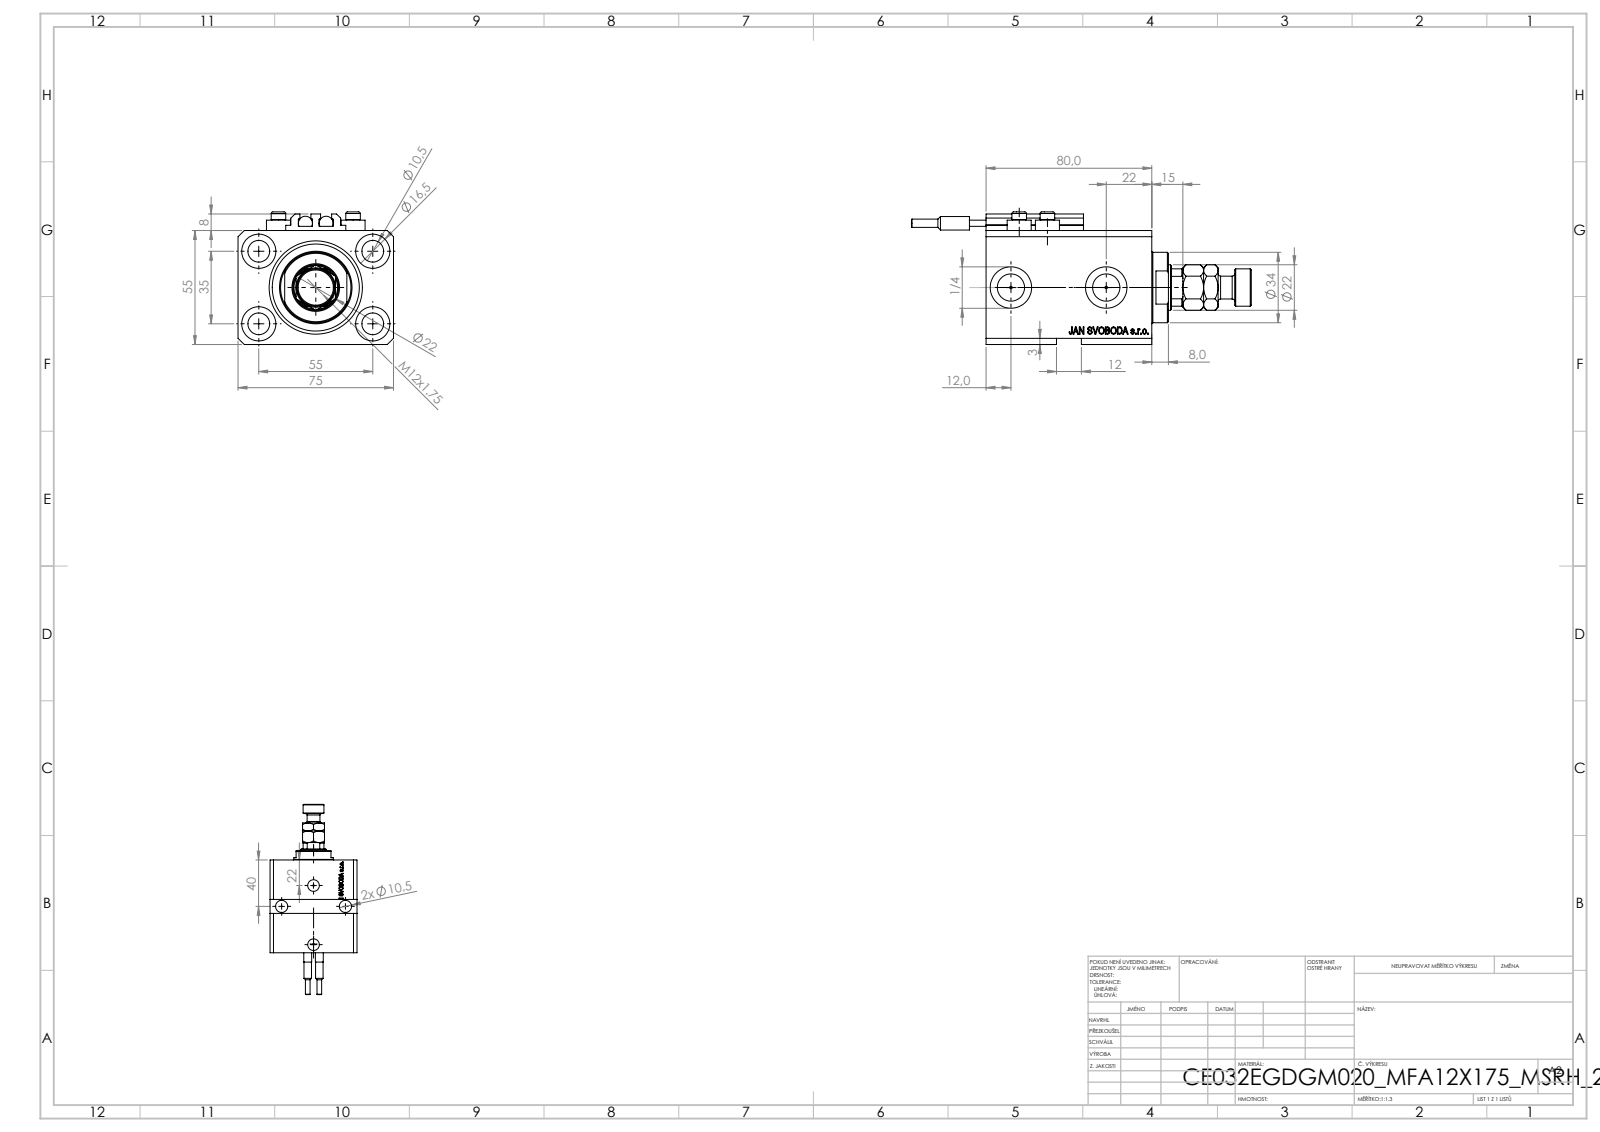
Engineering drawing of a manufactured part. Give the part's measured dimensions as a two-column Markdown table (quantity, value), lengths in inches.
| quantity | value |
| --- | --- |
| part name | V250CE_C_VCP; MFA; SWITCH_V250CE; V250CE_VC_E (+2 more) |
| STEP written by | SolidWorks 2019 (CONFIG_CONTROL_DESIGN) |
| units | inches |
| bodies | 11 solids, 1184 faces (566 planar, 154 cylindrical, 464 other) |
| overall size | 6.457 × 2.953 × 2.52 |
| volume | 17.81 in³ |
| surface area | 125.6 in² |
| round holes (diameter × count) | 0.413 × 7, 0.049 × 4, 0.157 × 4, 0.65 × 4, 0.394 × 2, 0.518 × 2, 0.787 × 2, 0.866 × 1, 1.26 × 1, 1.772 × 1 |
| round bosses / shafts (diameter × count) | 0.457 × 4, 0.276 × 4, 0.268 × 2, 0.256 × 2, 0.157 × 2, 1.339 × 1, 0.709 × 1, 0.433 × 1 |
| partial cylindrical surfaces (radius × count) | 0.008 × 10, 0.413 × 1 |
| main face-to-face distances | 2.165, 2.953, 0.591, 3.15, 2.559, 0.118, 0.39, 2.169, 2.244, 2.76 |
| hole center spacings | 1.283, 2.165, 0.535, 0.555, 0.783, 0.792, 1.016, 1.121 |
